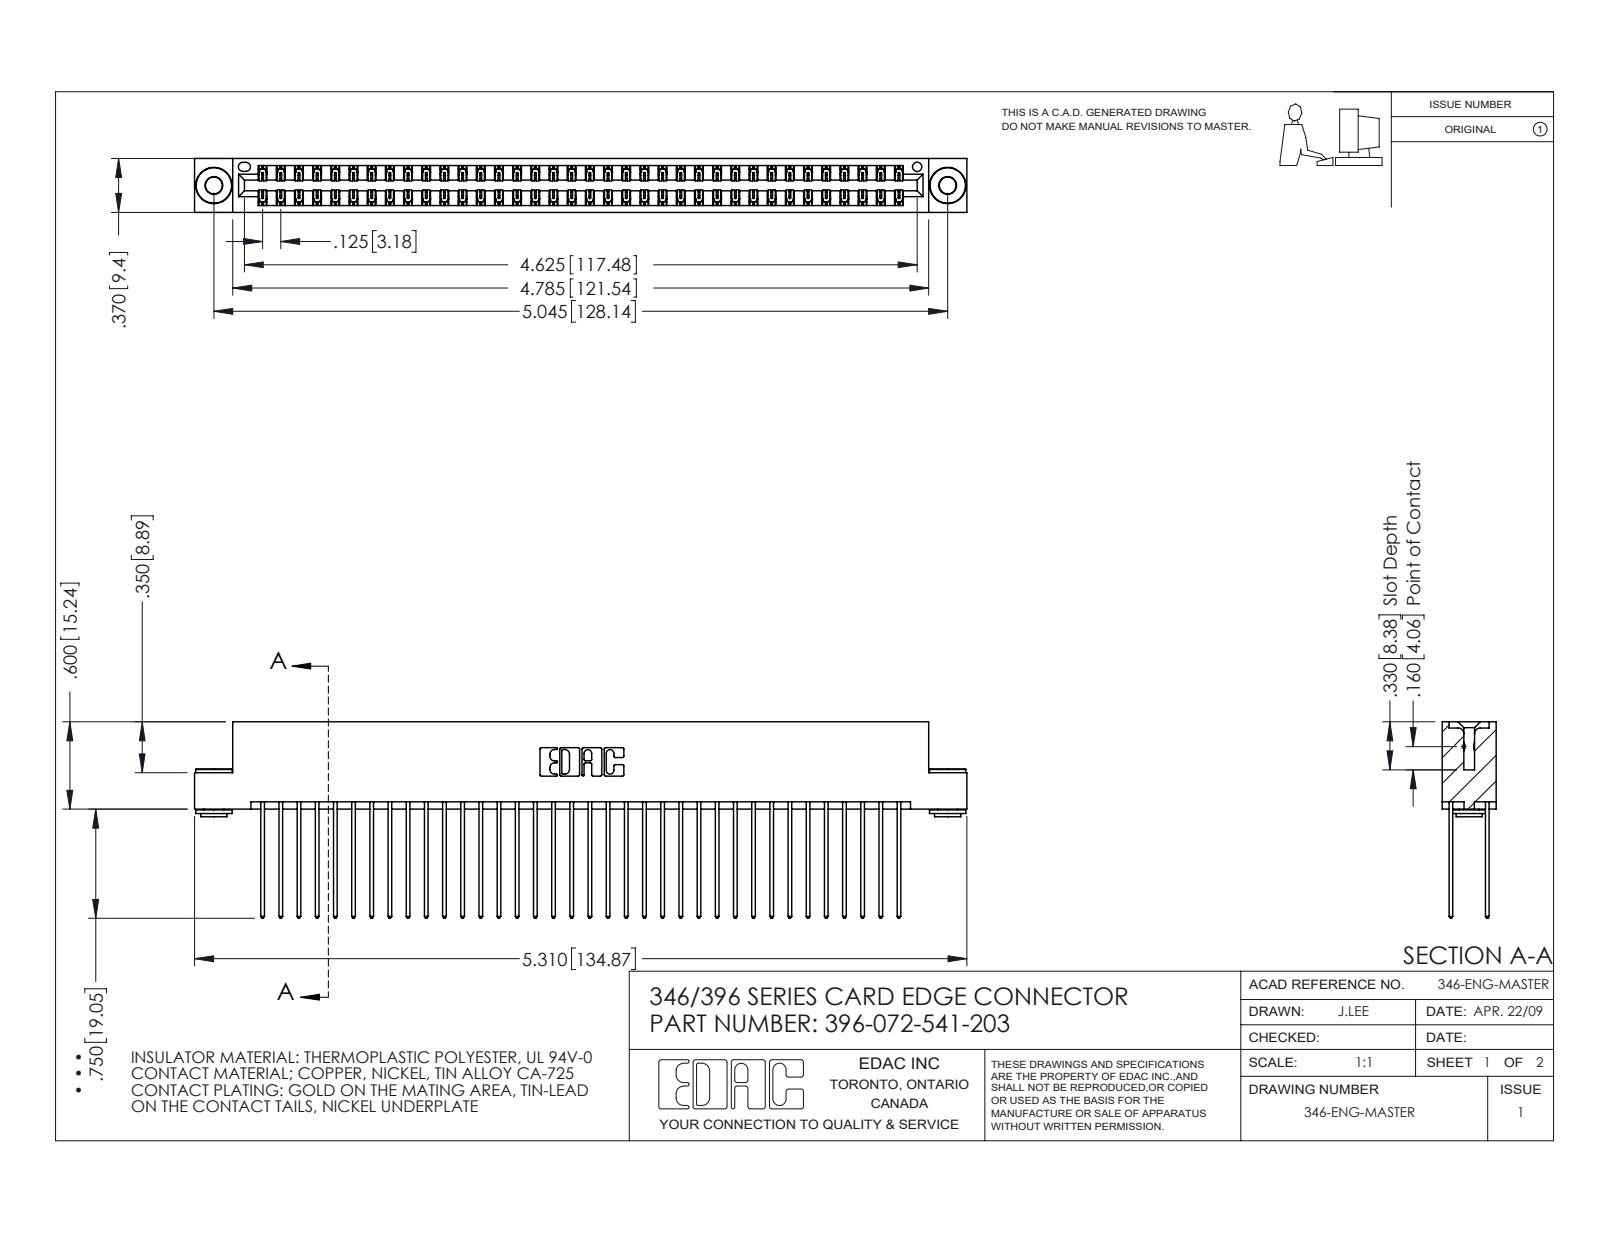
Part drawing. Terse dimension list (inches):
name: 345-292-001_345-293-141; 346 Part_Flush Mounting Lugs - 0.156 Dia-TH; 396-072-541-203; 345-250-002_345-250-002-102
written by: SolidWorks 2016 (CONFIG_CONTROL_DESIGN)
unit: in
bodies: 75 solids, 3904 faces (2606 planar, 1290 cylindrical, 8 other)
size: 5.31 × 1.35 × 0.37
volume: 0.826 in³; area: 32.1 in²
holes: 2× ⌀0.116, 2× ⌀0.156, 1× ⌀0.064
bosses: 2× ⌀0.25, 2× ⌀0.18, 2× ⌀0.136
rounds: 108× R0.006, 72× R0.01, 22× R0.01, 6× R0.007, 6× R0.031, 3× R0.026, 2× R0.014, 2× R0.022
face distances: 0.048, 0.322, 0.25, 0.025, 0.072, 0.298, 0.37, 0.275, 0.225, 0.148
hole spacings: 0.246, 4.836, 5.045
